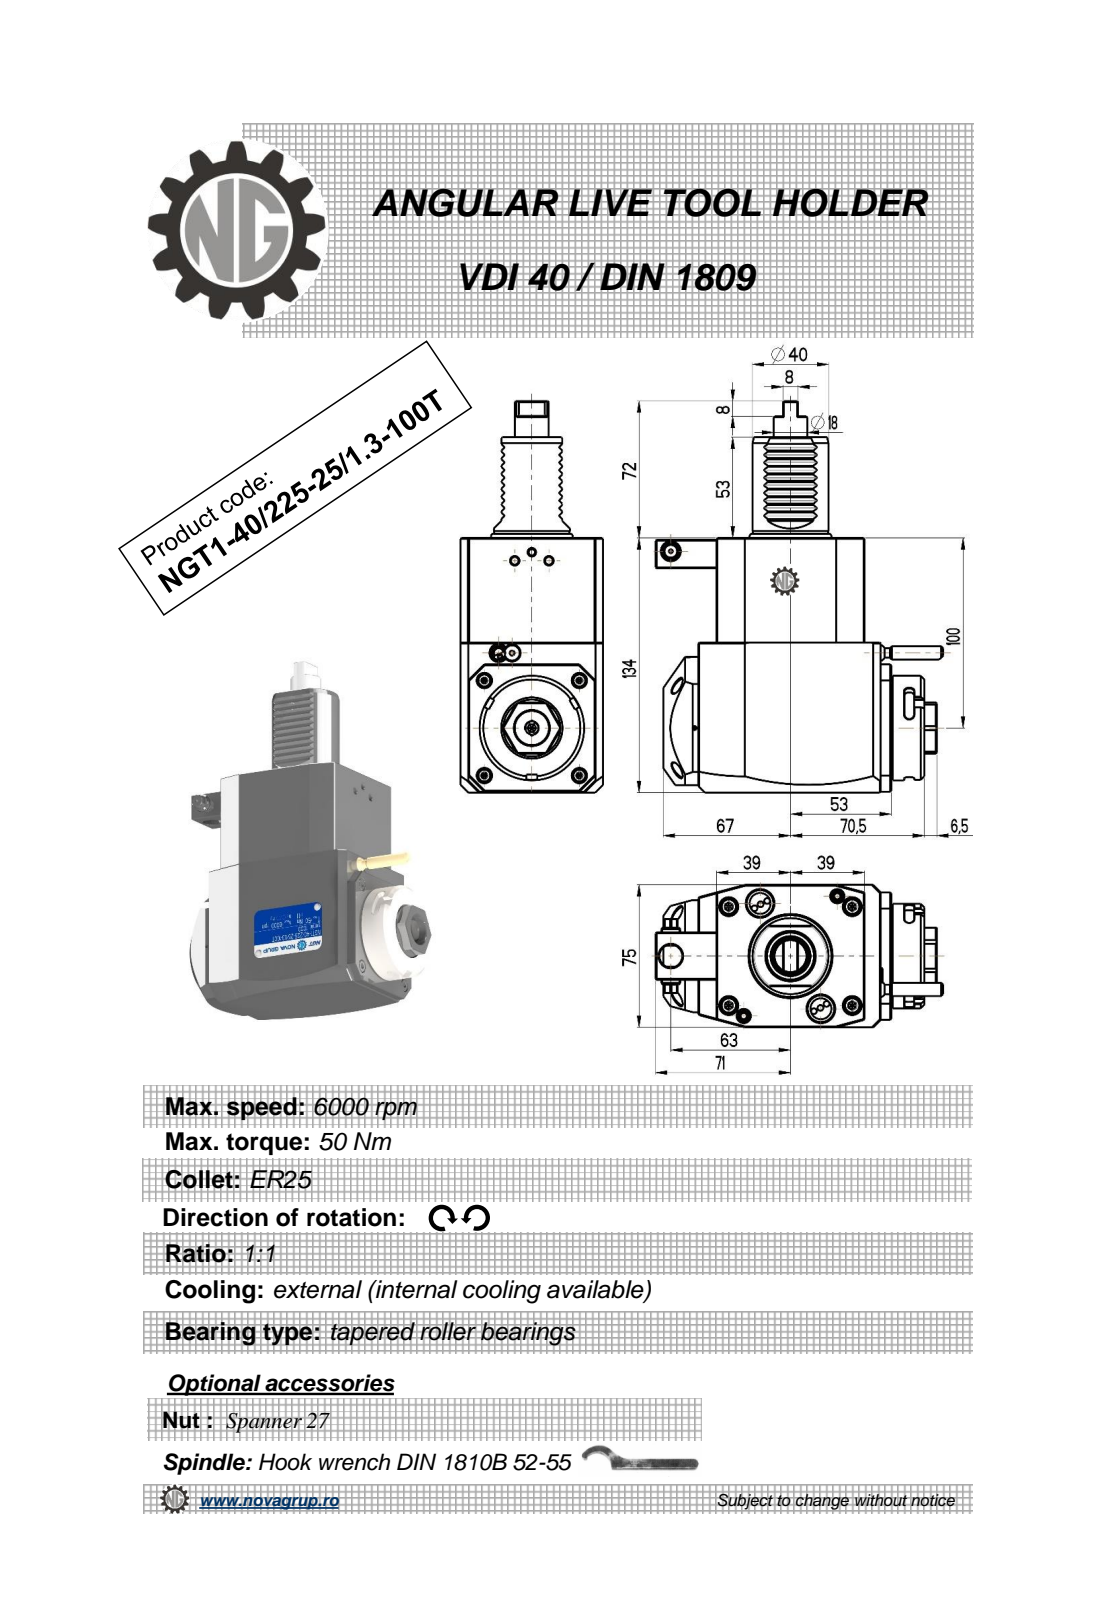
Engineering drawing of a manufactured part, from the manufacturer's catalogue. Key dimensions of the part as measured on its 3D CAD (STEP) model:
Part name (STEP PRODUCT): NGT1_40_225_25_1_3_100T
STEP written by: PRO/ENGINEER BY PARAMETRIC TECHNOLOGY CORPORATION, 2010280 (CONFIG_CONTROL_DESIGN)
Units: millimetres
Bodies: 1 solid, 388 faces (217 planar, 95 cylindrical, 76 other)
Overall size (bounding box): 206 × 151.33 × 75
Volume: 1 060 000 mm³ · Surface area: 76 588 mm²
Round holes (diameter × count): ⌀2 ×1, ⌀2.5 ×1, ⌀3 ×1, ⌀9.5 ×1, ⌀12 ×1, ⌀18 ×1
Round bosses / shafts (diameter × count): ⌀8 ×2, ⌀55 ×1, ⌀48 ×1, ⌀40 ×1, ⌀17.8 ×1, ⌀10 ×1, ⌀7 ×1, ⌀5 ×1
Partial cylindrical surfaces — rounded edges, fillets, slot ends (radius × count): R0.3 ×20, R2.5 ×6, R0.8 ×2, R180 ×2, R3.85 ×1, R4.25 ×1, R15 ×1, R24.5 ×1
Main face-to-face distances: 75, 134, 78, 14, 92, 17.5, 31.5, 84.88, 109.5, 54
Hole centre spacings: 43.2, 55.81, 92.5
